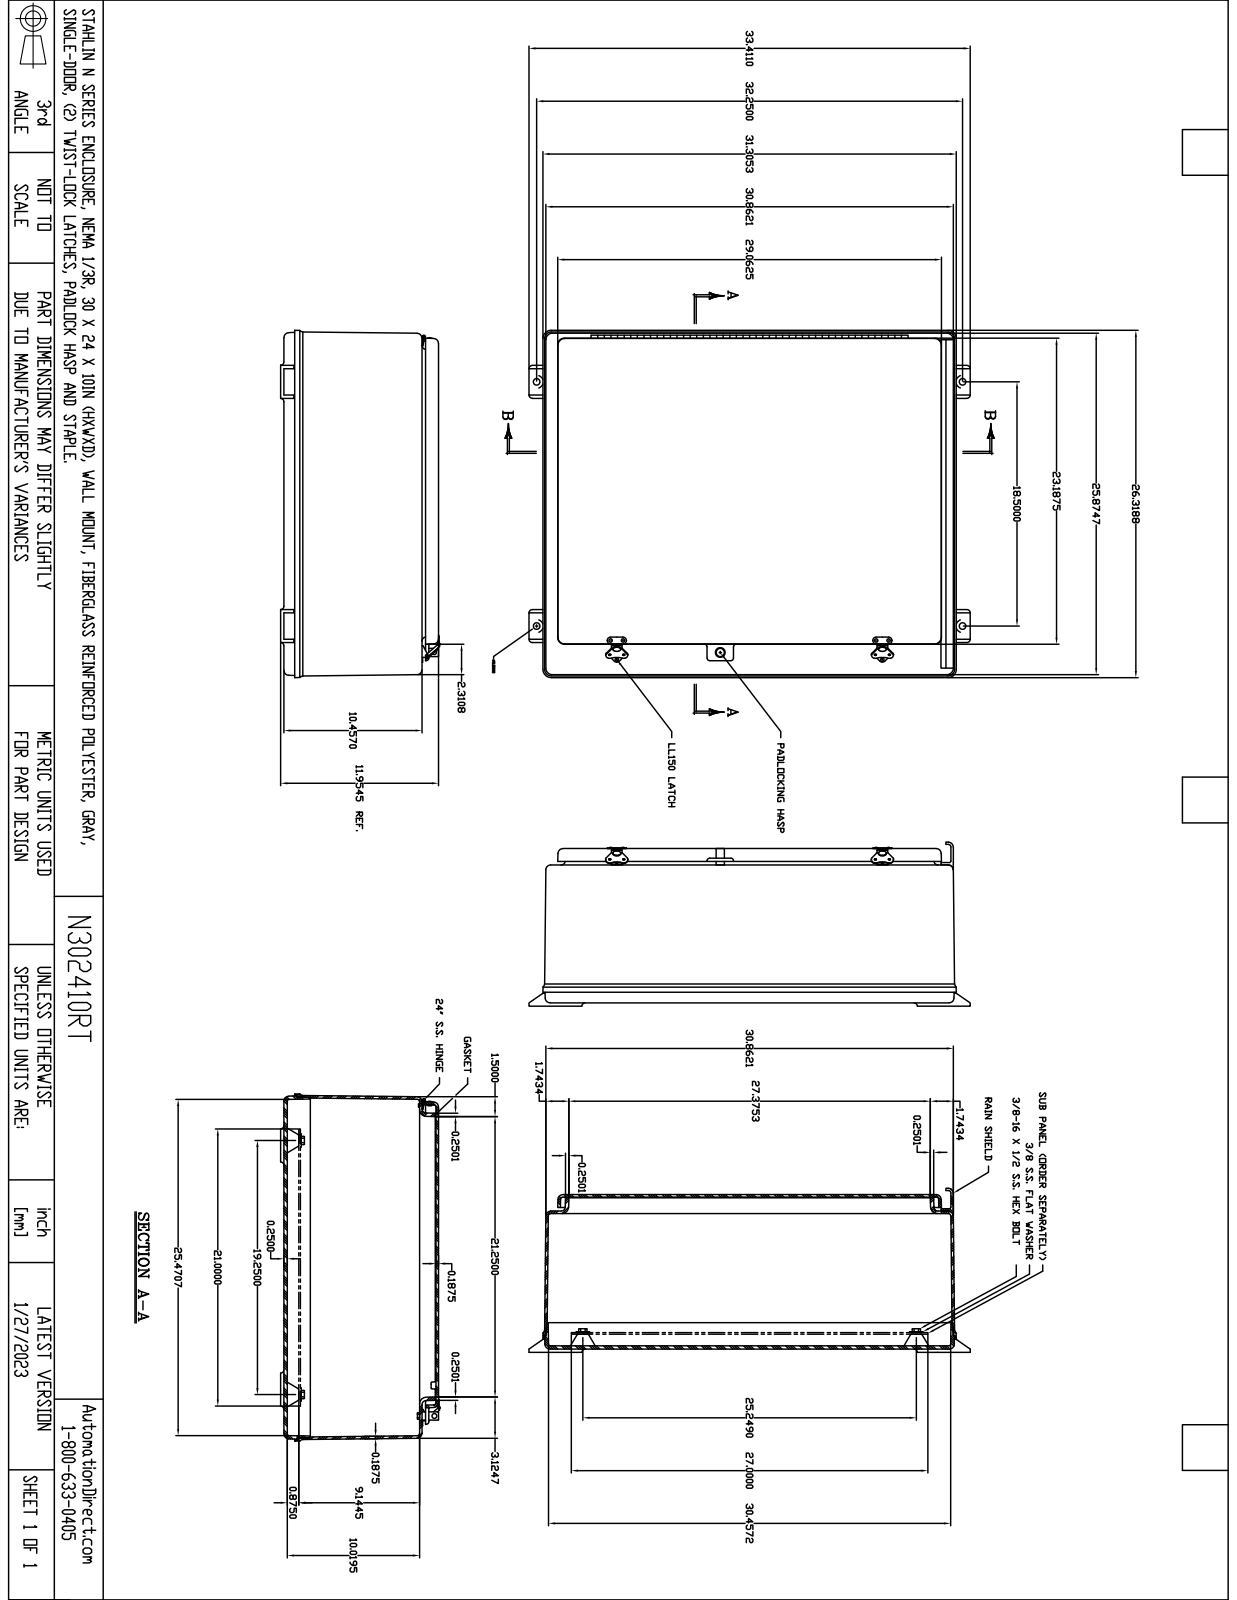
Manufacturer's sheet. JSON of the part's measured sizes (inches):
{"part_name": "T302410RT", "step_written_by": "SolidWorks 2018 (AUTOMOTIVE_DESIGN)", "units": "inches", "bodies": {"solids": 42, "faces": 1239, "planar": 495, "cylindrical": 484, "other": 260}, "overall_size": [33.406, 26.313, 12.469], "volume_in3": 657.1, "surface_area_in2": 6695, "round_holes": [[0.13, 21], [0.063, 8], [0.1, 8], [0.201, 8], [0.138, 4], [0.187, 4], [0.281, 4], [0.563, 4], [0.065, 2], [0.145, 2], [0.51, 2], [0.51, 2]], "round_bosses_or_shafts": [[0.357, 8], [0.187, 8], [0.14, 8], [0.297, 3], [0.5, 2], [0.25, 1], [0.201, 1], [0.2, 1]], "partial_cylinders_radius": [[0.01, 60], [0.25, 24], [0.187, 12], [0.375, 12], [0.5, 12], [0.188, 10], [0.313, 9], [0.03, 8]], "face_to_face_distances": [0.187, 0.25, 11.469, 11.719, 0.188, 11.53, 11.28, 1.25, 10.469, 10.281], "hole_center_spacings": [7.5, 15, 1.512, 3.489, 15.5, 20.125, 22.5, 28.707]}
